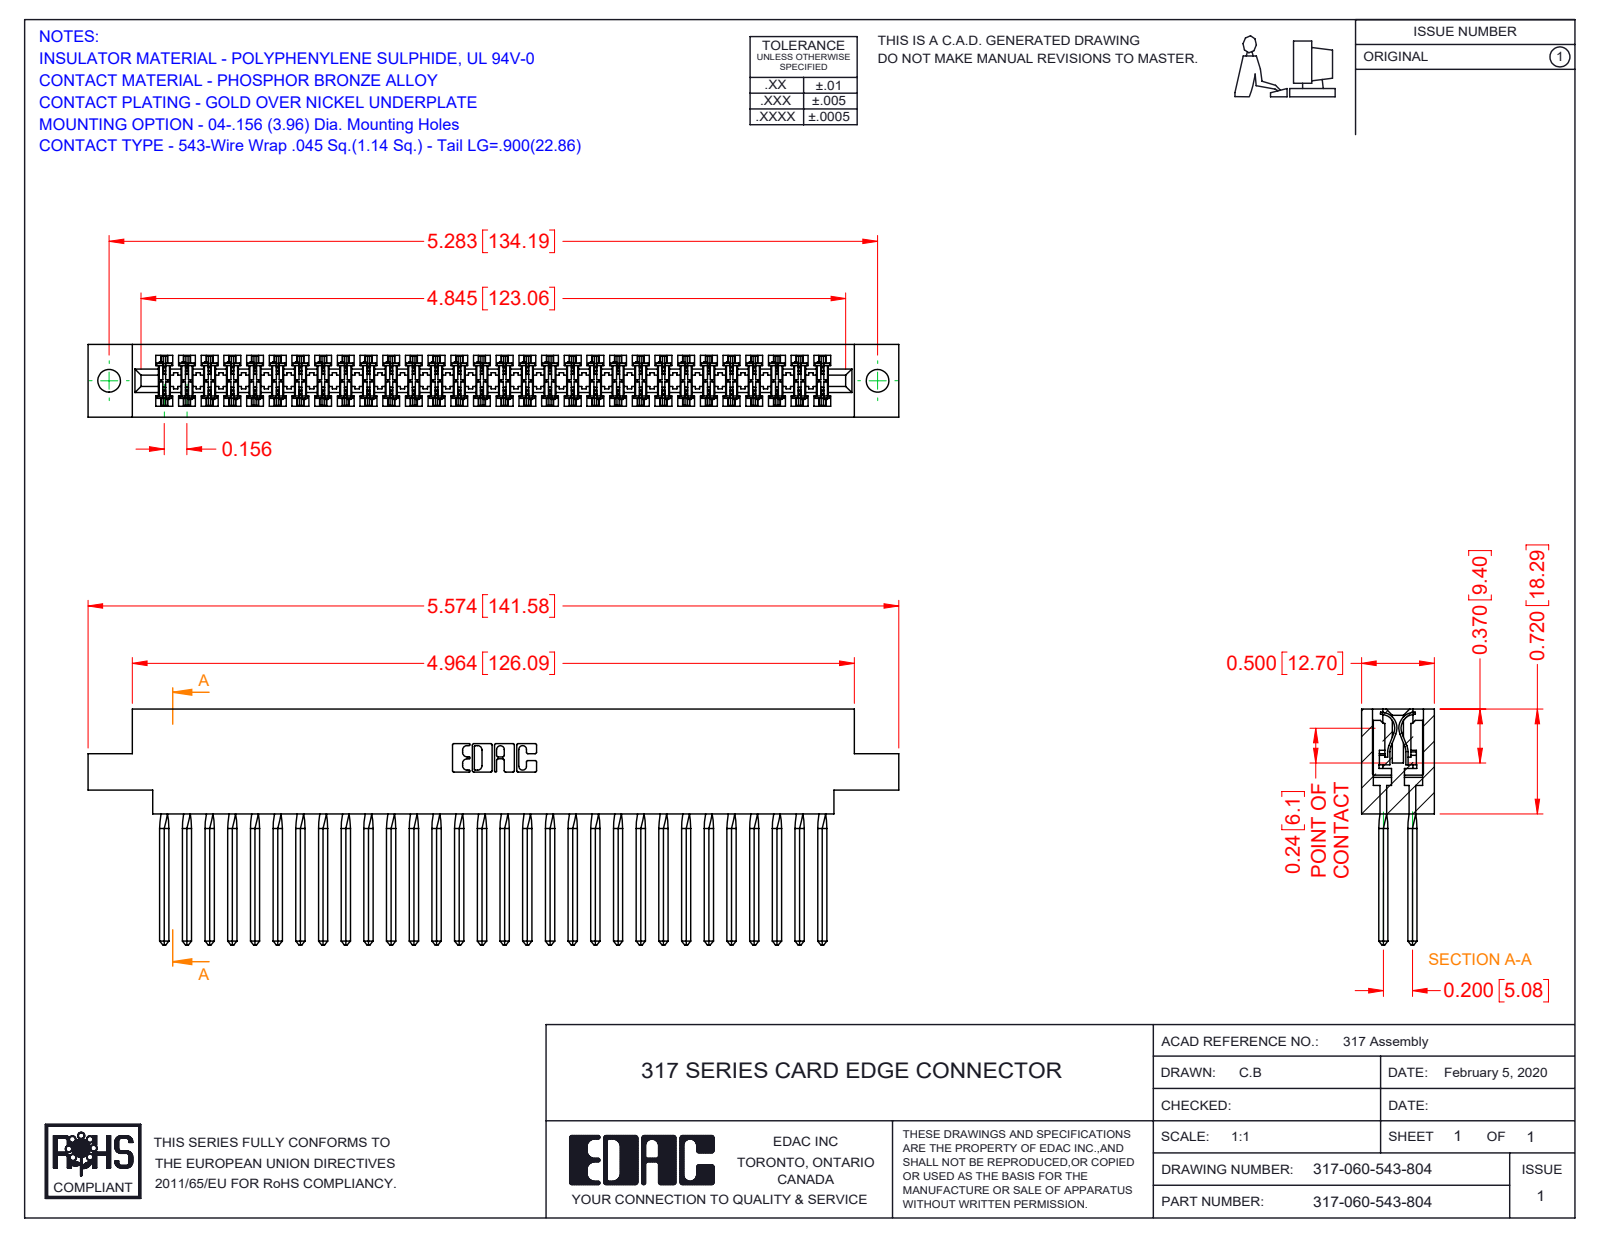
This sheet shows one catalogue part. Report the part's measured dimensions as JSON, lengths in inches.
{"part_name": "317-290-001_543; 317 Part_.156 Dia - TH; 317-060-543-804", "step_written_by": "SolidWorks 2016 (CONFIG_CONTROL_DESIGN)", "units": "inches", "bodies": {"solids": 61, "faces": 5442, "planar": 4438, "cylindrical": 764, "other": 240}, "overall_size": [5.574, 1.62, 0.5], "volume_in3": 1.438, "surface_area_in2": 54.42, "round_holes": [[0.156, 2]], "partial_cylinders_radius": [[0.015, 120], [0.01, 22], [0.007, 6], [0.031, 6], [0.026, 3], [0.095, 2], [0.1, 2], [0.11, 2]], "face_to_face_distances": [0.5, 0.075, 0.425, 0.35, 0.11, 0.195, 0.094, 0.2, 0.72, 0.115], "hole_center_spacings": [5.283]}
